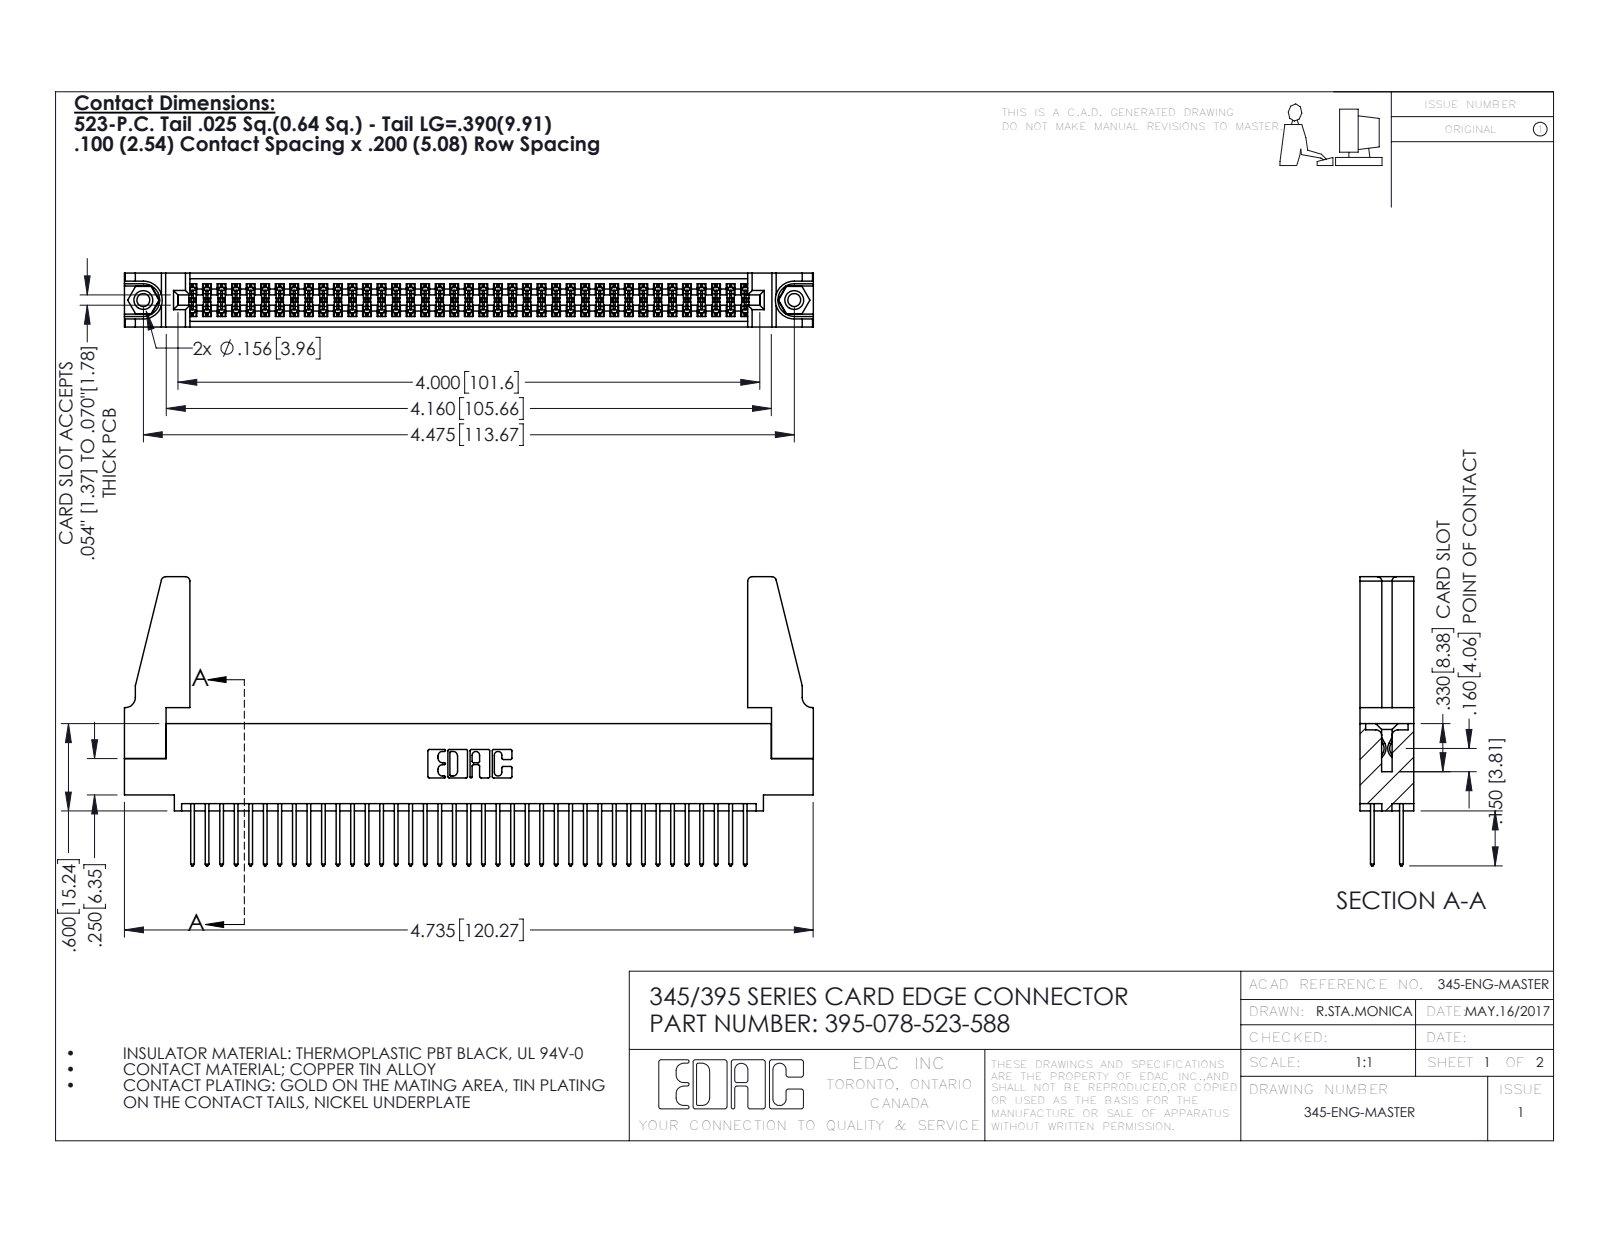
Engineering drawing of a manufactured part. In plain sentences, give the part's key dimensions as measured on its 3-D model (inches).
The part is named "345-292-001_345-293-123; 395-078-523-588; 345-250-001_345-250-001-102; 345 Part_0.110 Offset - 0.156 Dia-TH (+1 more)". Its 3-D file was written by "SolidWorks 2016 (CONFIG_CONTROL_DESIGN)". It is 83 solids with 4154 faces: 2730 planar, 1408 cylindrical and 16 other. Overall it measures 4.736 by 1.987 by 0.37 inches. Its volume is 0.915 cubic inches and its surface area 32.91 square inches. Round holes: 2 of diameter 0.089, 2 of diameter 0.125, 2 of diameter 0.156, 1 of diameter 0.064. Round bosses or shafts: 2 of diameter 0.155. Partial cylindrical surfaces (rounded edges, fillets, slot ends): 117 of radius 0.006, 78 of radius 0.01, 22 of radius 0.01, 8 of radius 0.03, 6 of radius 0.007, 6 of radius 0.031, 3 of radius 0.026, 2 of radius 0.014. The main face-to-face distances are 0.072, 0.298, 0.37, 0.2, 0.098, 0.272, 0.025, 0.225, 0.175, 0.149. The hole center spacings are 0.27, 4.239, 4.475.
